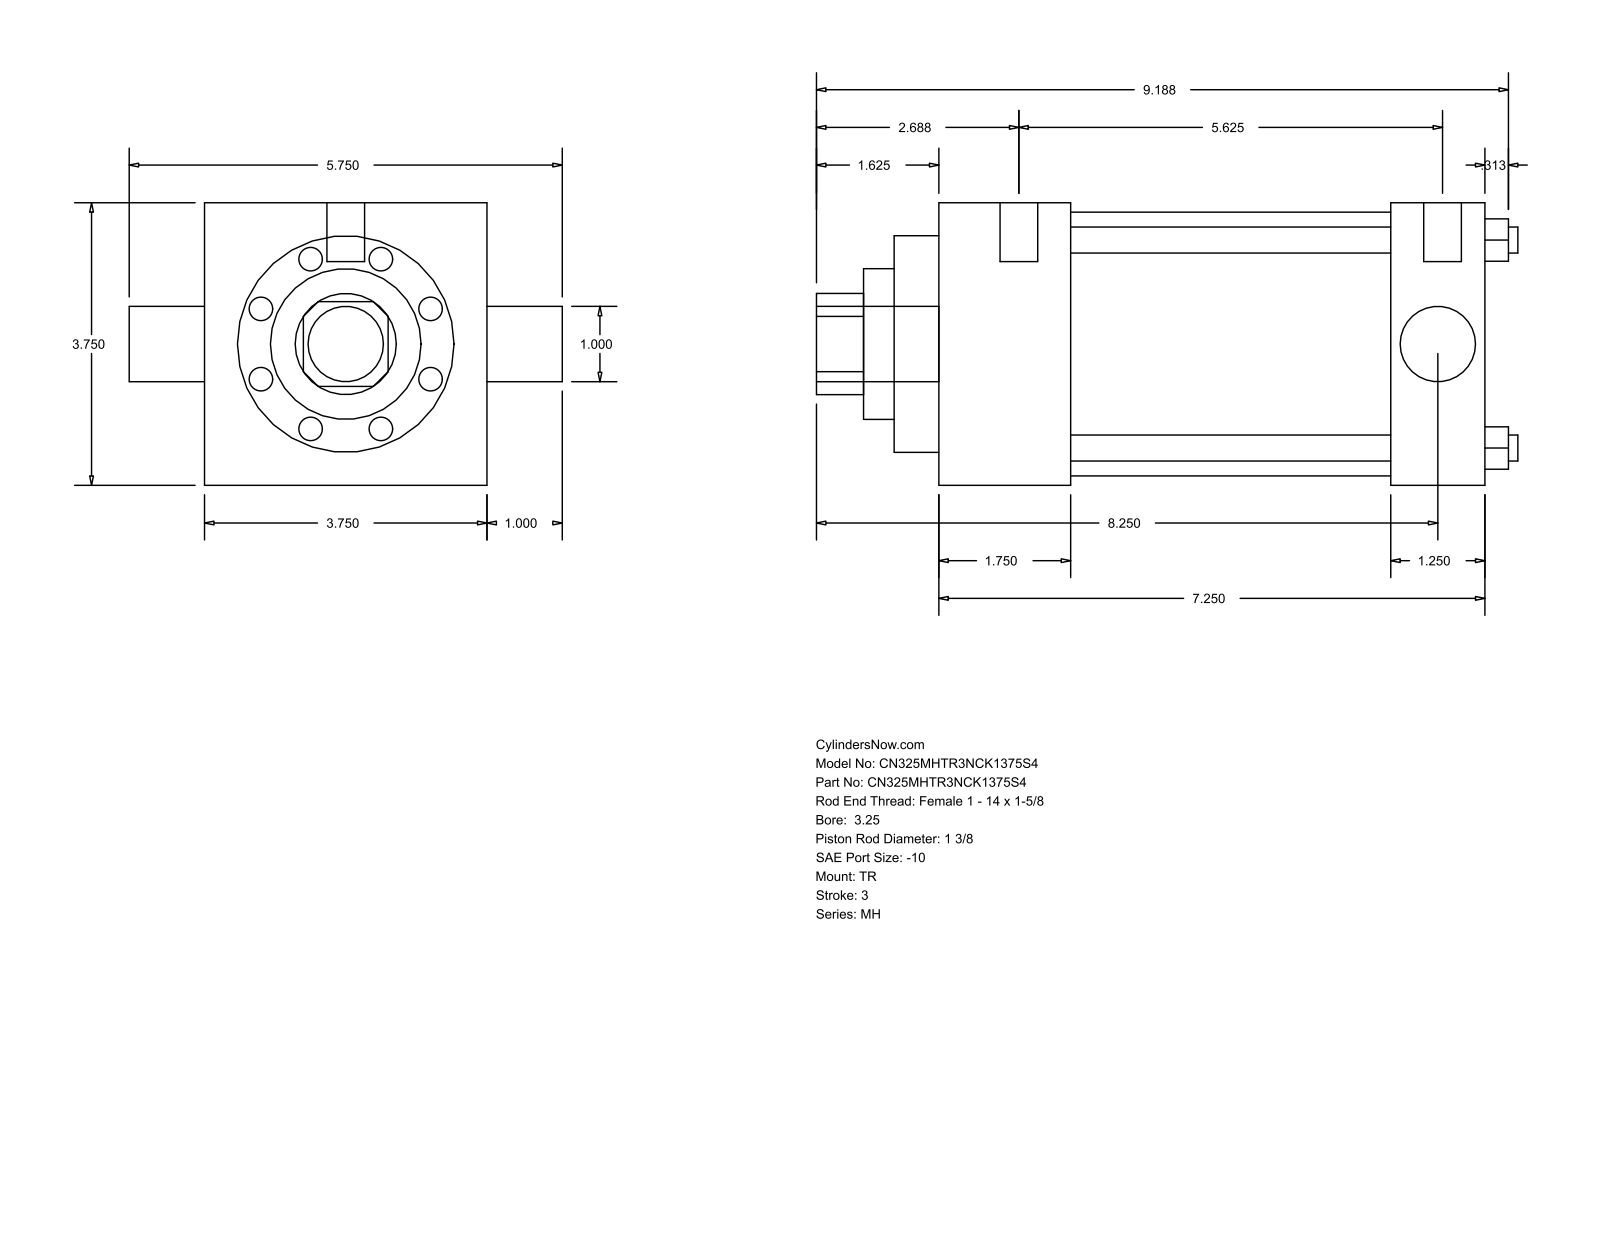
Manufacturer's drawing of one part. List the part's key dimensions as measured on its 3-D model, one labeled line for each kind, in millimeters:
Part name (STEP PRODUCT): MH_TR__0325_1.375
STEP written by: GSSL Pune (CONFIG_CONTROL_DESIGN)
Units: millimetres
Bodies: 0 solids, 86 faces (61 planar, 25 cylindrical, 0 other)
Overall size (bounding box): 236.54 × 146.05 × 95.25
Round holes (diameter × count): ⌀8.76 ×4, ⌀25.4 ×1, ⌀34.92 ×1, ⌀50.8 ×1, ⌀73.03 ×1, ⌀88.9 ×1
Round bosses / shafts (diameter × count): ⌀5.56 ×3, ⌀12.7 ×2, ⌀25.4 ×1
Partial cylindrical surfaces — rounded edges, fillets, slot ends (radius × count): R17.06 ×1
Main face-to-face distances: 95.24, 184.16, 44.45, 152.41, 107.96, 139.71, 31.75, 15.08, 59.53, 167.49
Hole centre spacings: 49.57, 70.1, 99.14
